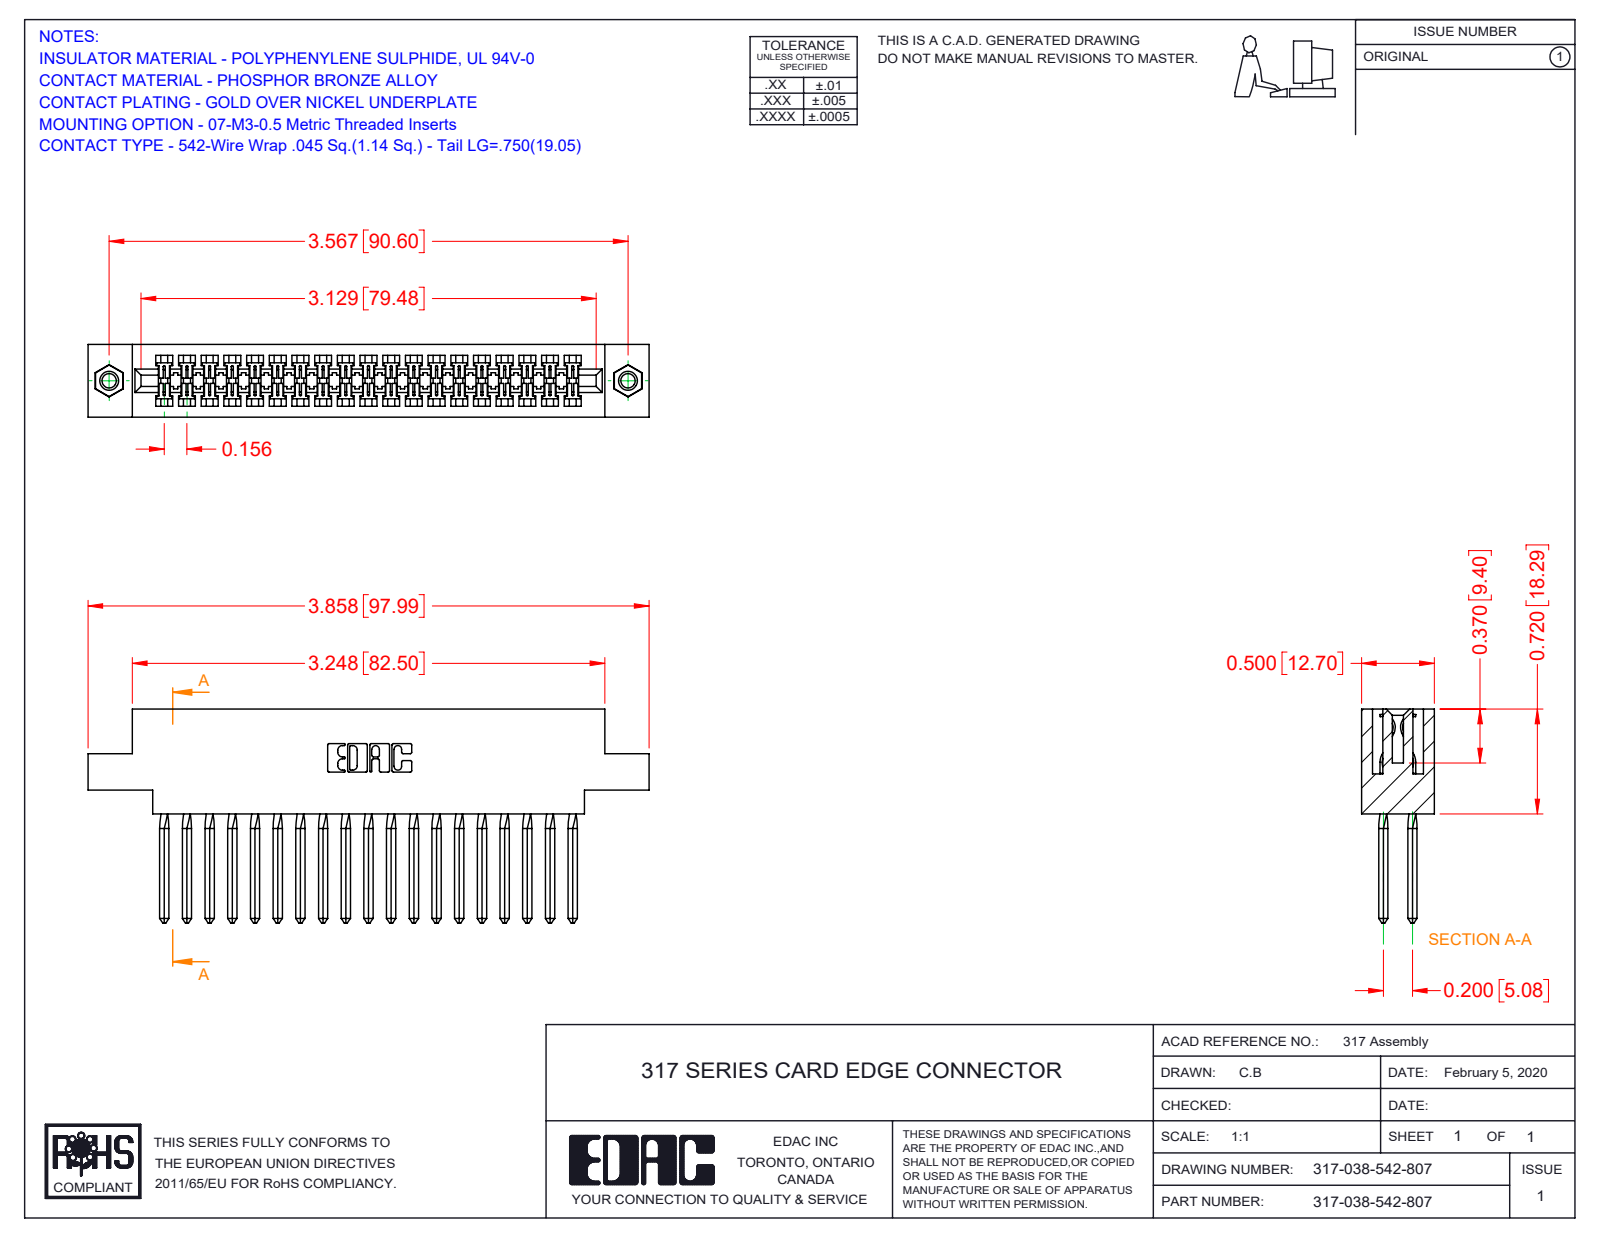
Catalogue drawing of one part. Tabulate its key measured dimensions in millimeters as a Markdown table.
| quantity | value |
| --- | --- |
| part name | 345-250-001_345-250-005-103; 317-038-542-807; 317 Part_.156 Dia - TI; 317-290-003_542 |
| STEP written by | SolidWorks 2016 (CONFIG_CONTROL_DESIGN) |
| units | millimeters |
| bodies | 41 solids, 2328 faces (1838 planar, 322 cylindrical, 168 other) |
| overall size | 98 × 37.3 × 12.7 |
| volume | 15 300 mm³ |
| surface area | 20 580 mm² |
| round holes (diameter × count) | 2.5 × 2, 3.2 × 2, 4 × 2 |
| round bosses / shafts (diameter × count) | 3.9 × 2 |
| partial cylindrical surfaces (radius × count) | 0.2 × 76, 0.3 × 22, 0.2 × 6, 0.8 × 6, 0.7 × 3, 1.9 × 2, 2.3 × 2, 2.5 × 2 |
| main face-to-face distances | 12.7, 1.9, 10.8, 2.8, 8.9, 5.1, 2.9, 3.5, 18.3, 1.2 |
| hole center spacings | 90.6 |
